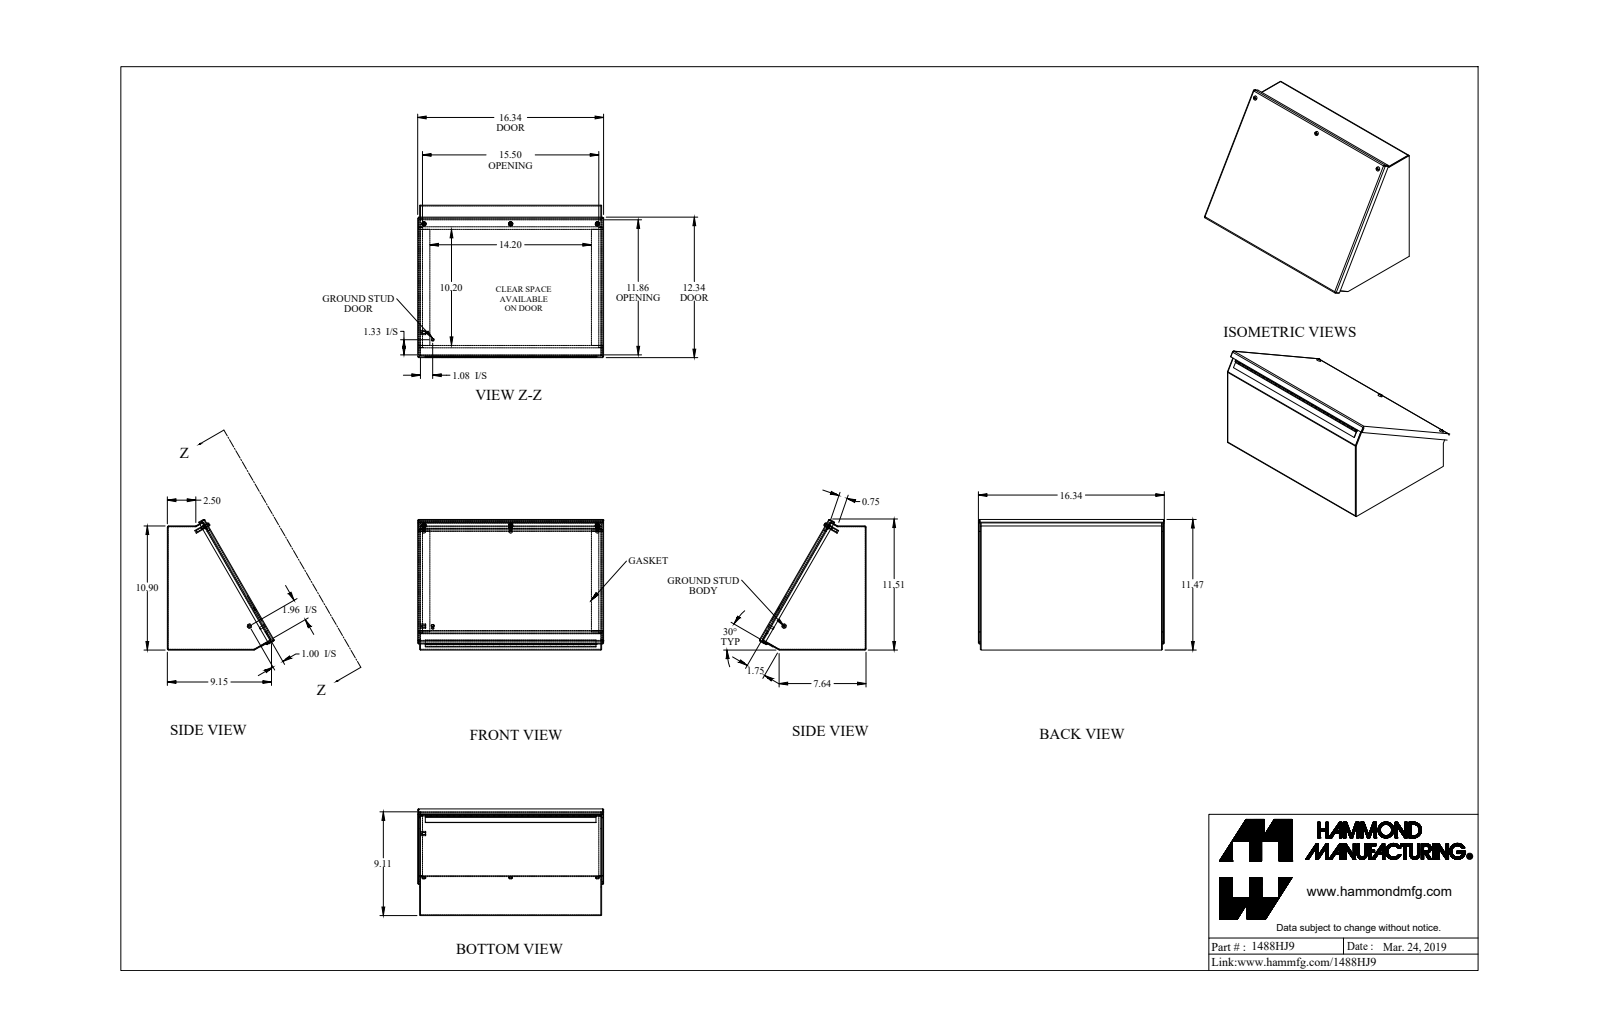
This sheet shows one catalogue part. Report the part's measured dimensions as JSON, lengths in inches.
{"part_name": "1488HJ9_Default", "step_written_by": "SolidWorks 2019 (CONFIG_CONTROL_DESIGN)", "units": "inches", "bodies": {"solids": 22, "faces": 638, "planar": 381, "cylindrical": 221, "other": 36}, "overall_size": [16.343, 11.472, 9.372], "volume_in3": 68.79, "surface_area_in2": 1722, "round_holes": [[0.159, 3], [0.25, 3], [0.05, 1], [0.156, 1]], "round_bosses_or_shafts": [[0.39, 3], [0.275, 3], [0.19, 3], [0.148, 3], [0.375, 1], [0.25, 1], [0.188, 1], [0.1, 1]], "partial_cylinders_radius": [[0.036, 12], [0.108, 12], [0.125, 3], [0.16, 3], [0.171, 3], [0.055, 1], [0.057, 1]], "face_to_face_distances": [0.072, 15.928, 10.828, 15.856, 16, 0.072, 0.125, 0.197, 10.9, 10.756], "hole_center_spacings": [7.625, 7.625, 15.25, 15.25, 2.224]}
